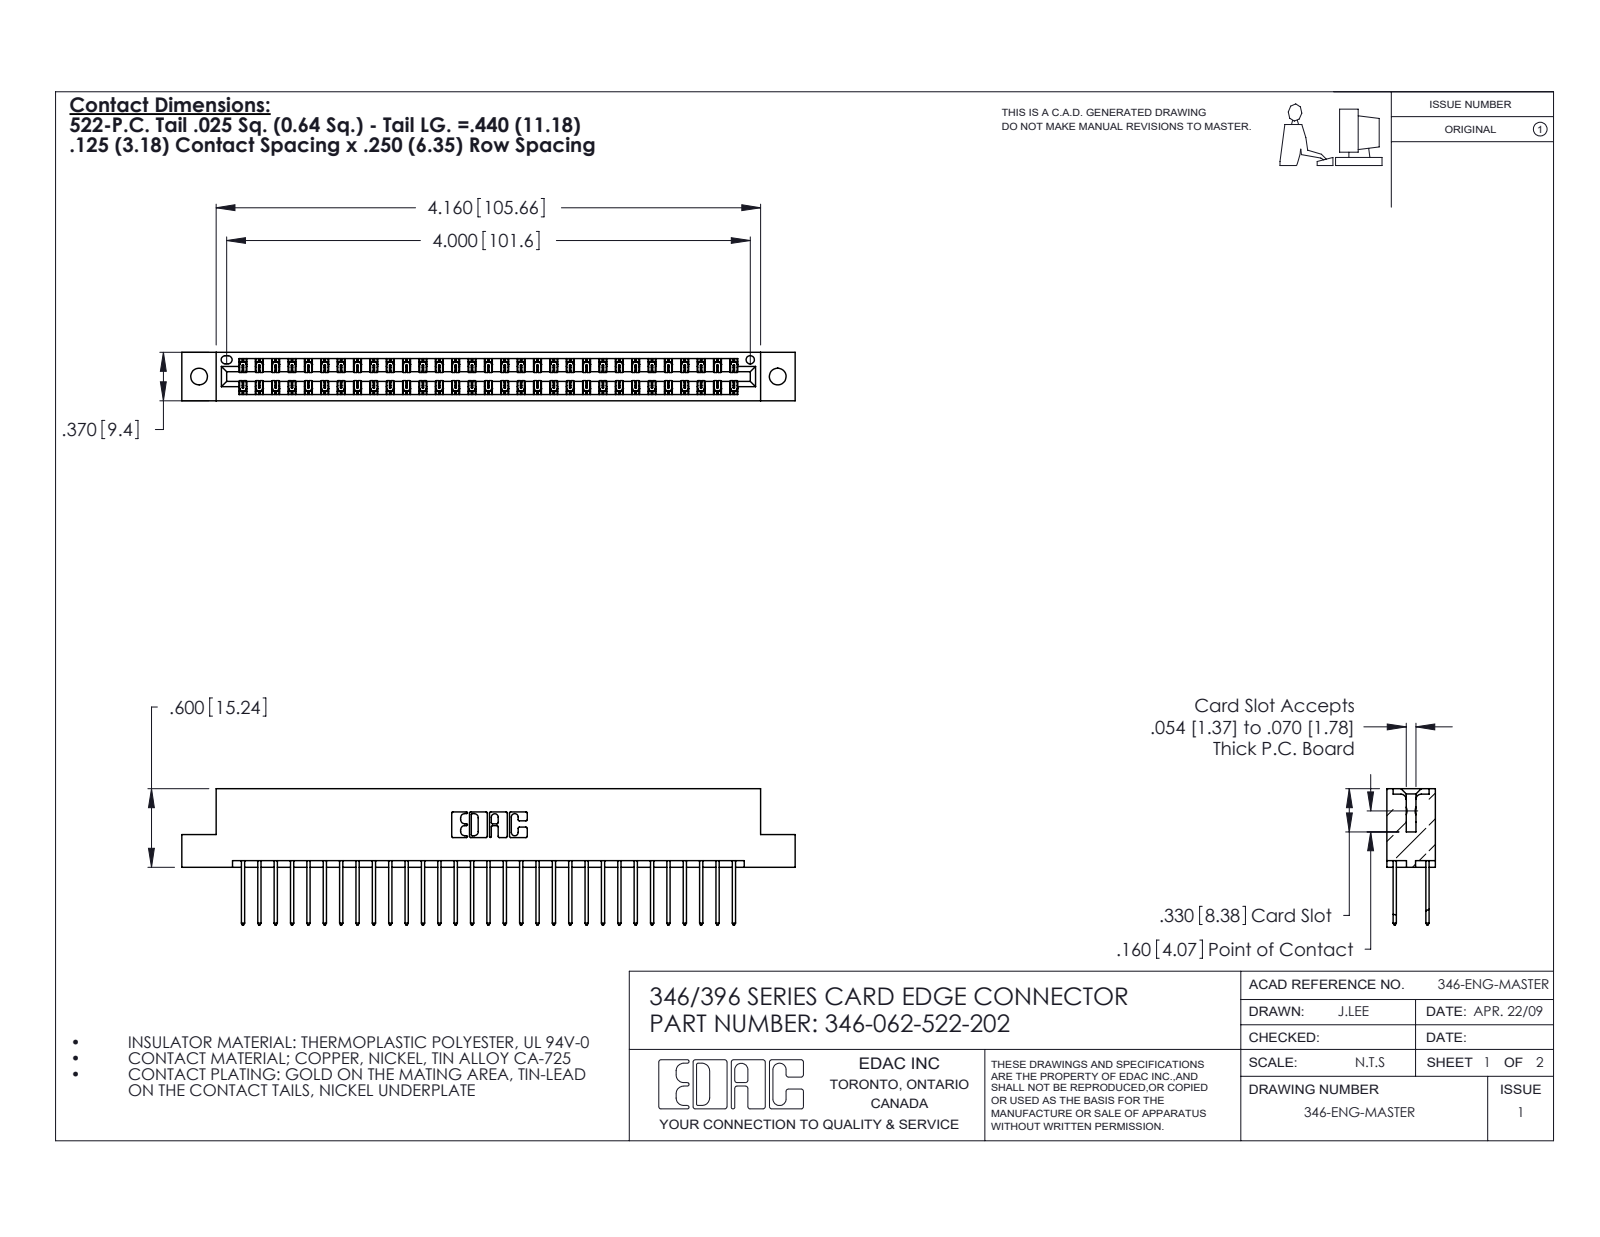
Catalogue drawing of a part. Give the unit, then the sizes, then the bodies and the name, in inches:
Units: inches
Overall size (bounding box): 4.685 × 1.04 × 0.37
Round holes (diameter × count): ⌀0.128 ×2, ⌀0.064 ×1
Partial cylindrical surfaces — rounded edges, fillets, slot ends (radius × count): R0.006 ×93, R0.01 ×62, R0.01 ×22, R0.007 ×6, R0.031 ×6, R0.026 ×3, R0.014 ×2, R0.022 ×2
Main face-to-face distances: 0.048, 0.322, 0.25, 0.37, 0.072, 0.298, 0.025, 0.275, 0.148, 0.222
Hole centre spacings: 0.246, 4.212, 4.42
Volume: 0.71 in³ · Surface area: 25.26 in²
Bodies: 63 solids, 3346 faces (2246 planar, 1100 cylindrical, 0 other)
Part name (STEP PRODUCT): 345-292-001_345-293-122; 346-062-522-202; 346 Part_Flush Mounting Lugs - 0.128 Dia
STEP written by: SolidWorks 2020 (CONFIG_CONTROL_DESIGN)
